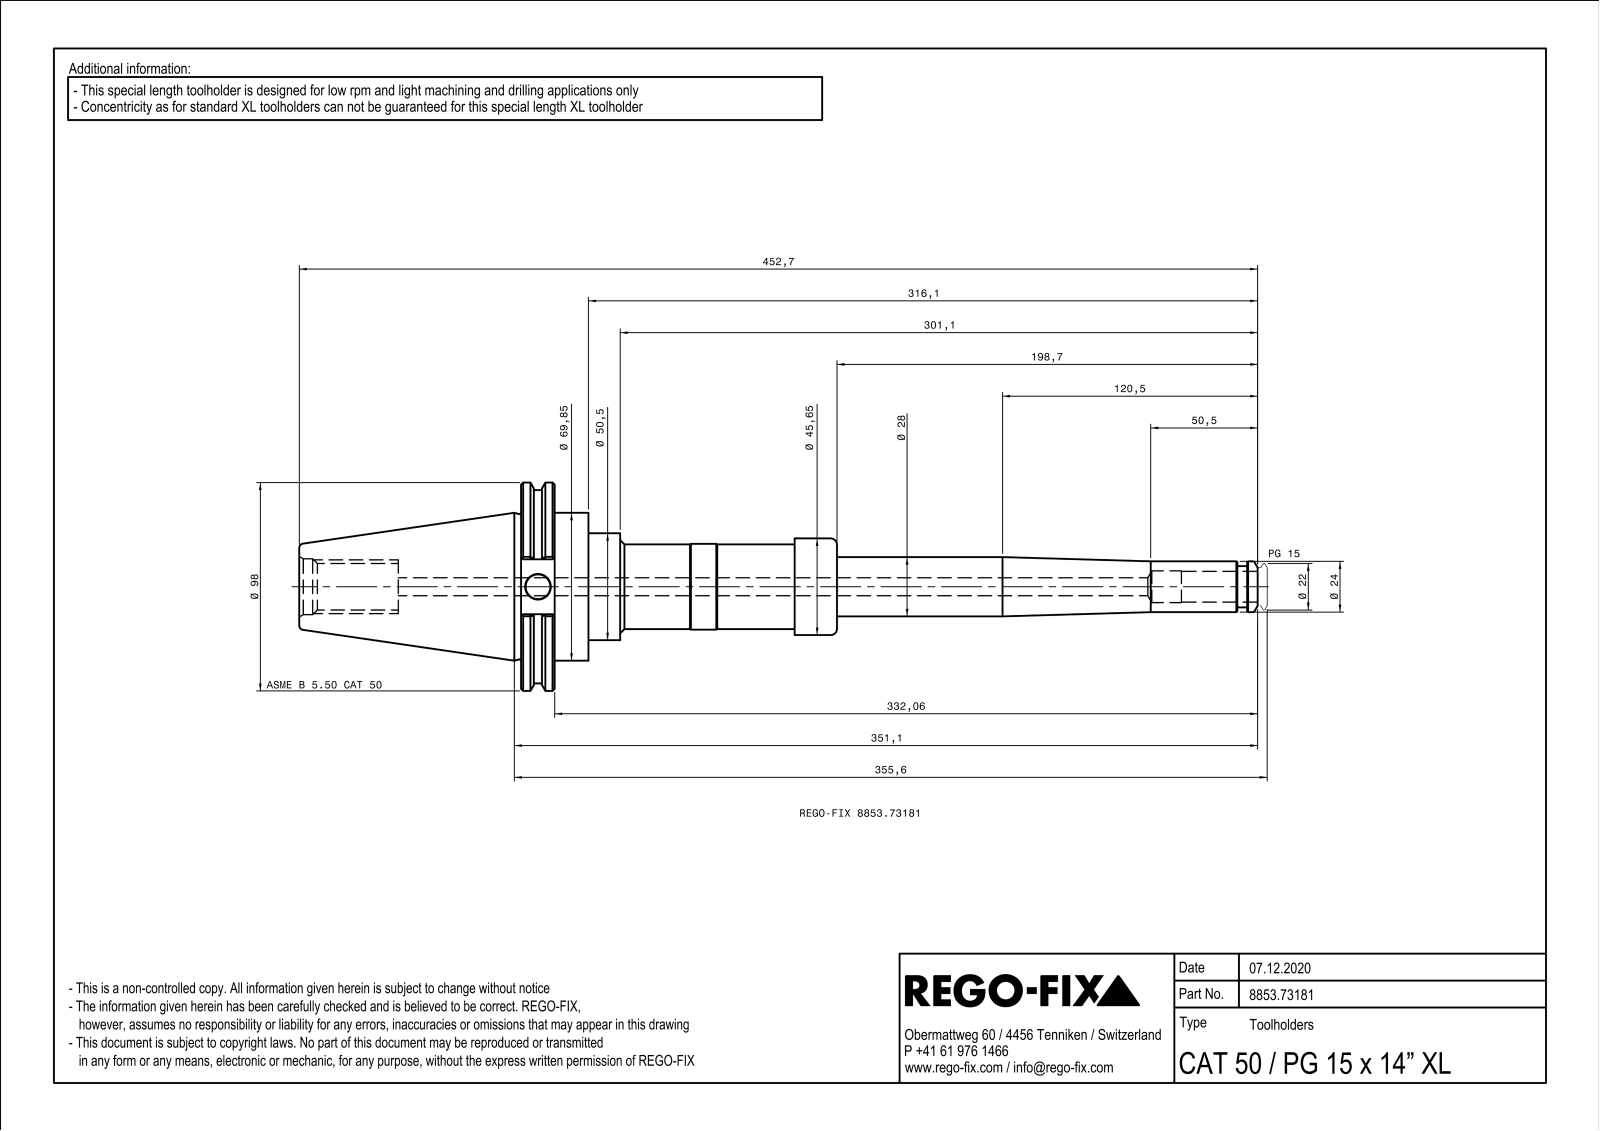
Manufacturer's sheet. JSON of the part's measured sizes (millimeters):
{"part_name": "NOCUT", "step_written_by": "SIEMENS PLM Software Solid Edge ST10 (AUTOMOTIVE_DESIGN)", "units": "millimeters", "bodies": {"solids": 1, "faces": 171, "planar": 48, "cylindrical": 46, "other": 77}, "overall_size": [452.7, 98.42, 94.39], "volume_mm3": 587443, "surface_area_mm2": 101679, "round_holes": [[9, 1], [10, 1], [11.7, 1], [13, 1], [15, 1], [21.96, 1], [25, 1], [26.4, 1], [29, 1], [38.38, 1], [40.05, 1], [43.3, 1]], "round_bosses_or_shafts": [[98.42, 1], [91.3, 1], [69.85, 1], [50.5, 1], [45.65, 1], [40.5, 1], [40, 1], [34, 1]], "partial_cylinders_radius": [[0.5, 12], [22.77, 1]], "face_to_face_distances": [15.87, 15.96, 31.83, 117.4, 133.36, 149.23, 6, 14, 254, 136.6]}
